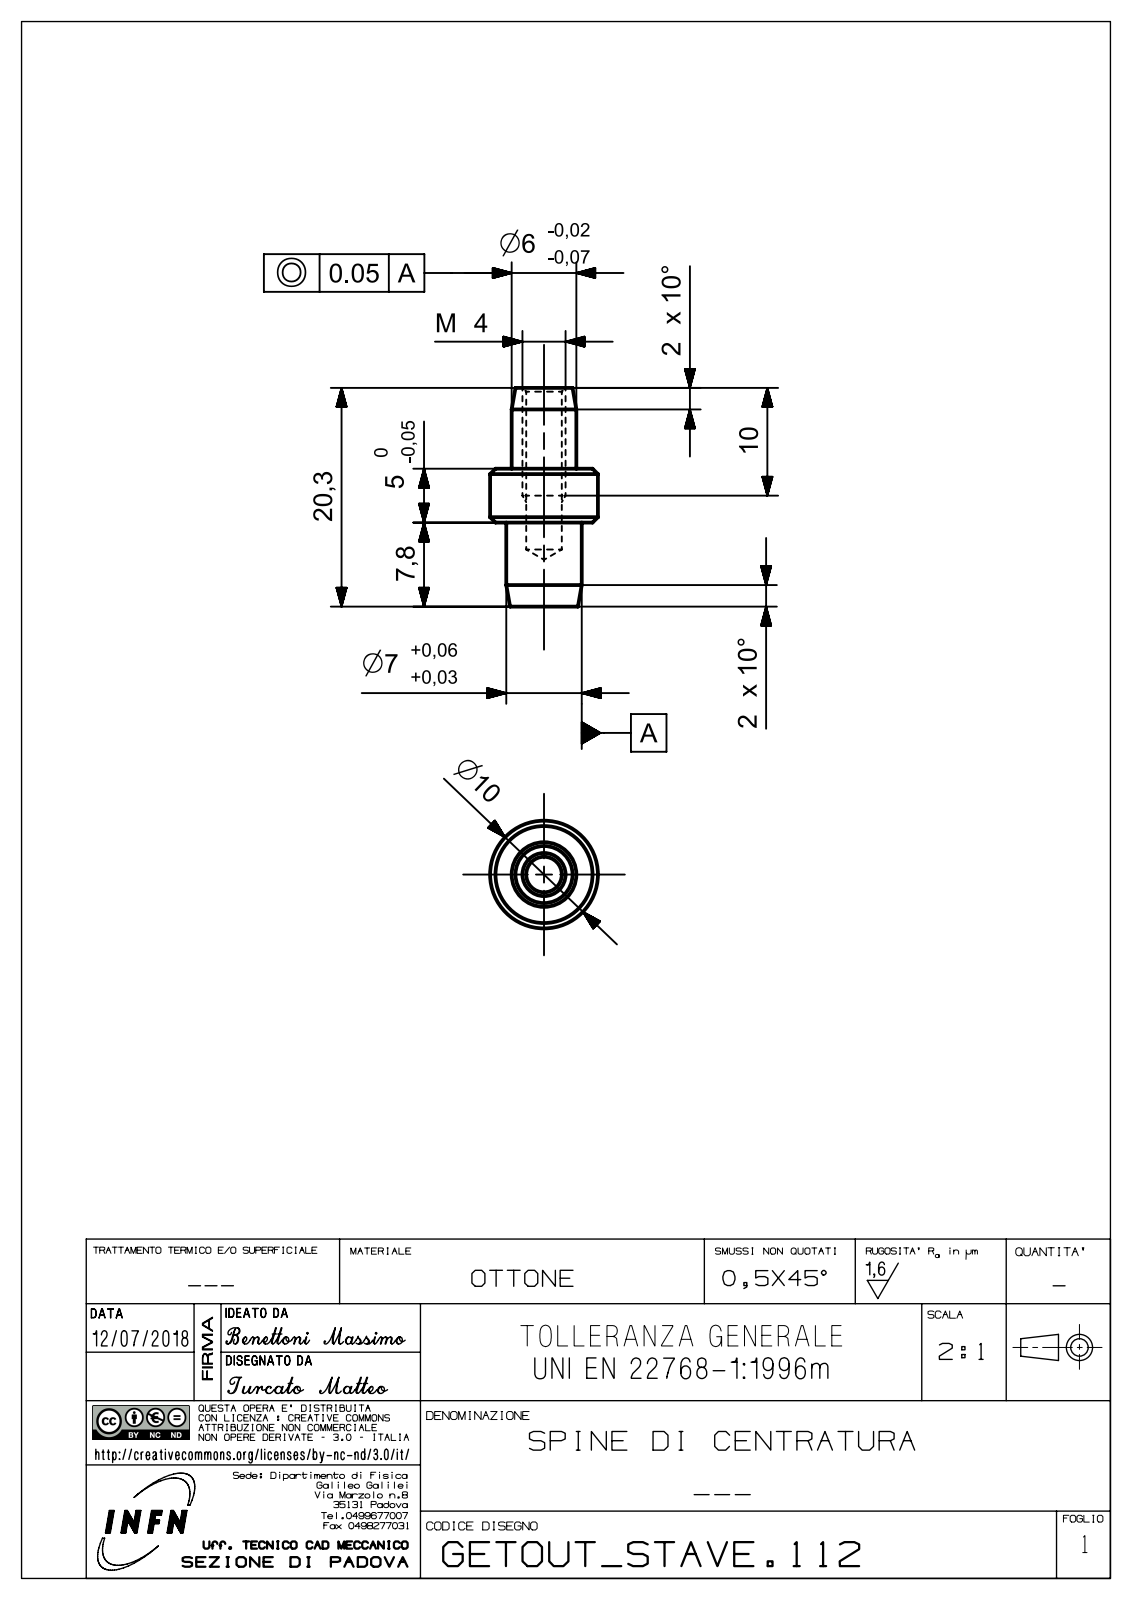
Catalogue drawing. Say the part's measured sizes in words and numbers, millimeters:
The part is named "bezA730AE56cd1p". Its 3-D file was written by "SIEMENS PLM Software NX 12.0 (AUTOMOTIVE_DESIGN)". It is 1 solid with 14 faces: 4 planar, 4 cylindrical and 6 other. Overall it measures 20.3 by 10 by 10 millimeters. Its volume is 752 cubic millimeters and its surface area 746 square millimeters. Round holes: 1 of diameter 3.3. Round bosses or shafts: 1 of diameter 10, 1 of diameter 7, 1 of diameter 6. The main face-to-face distances are 12.8, 7.8, 5, 20.3, 12.5, 7.5.
